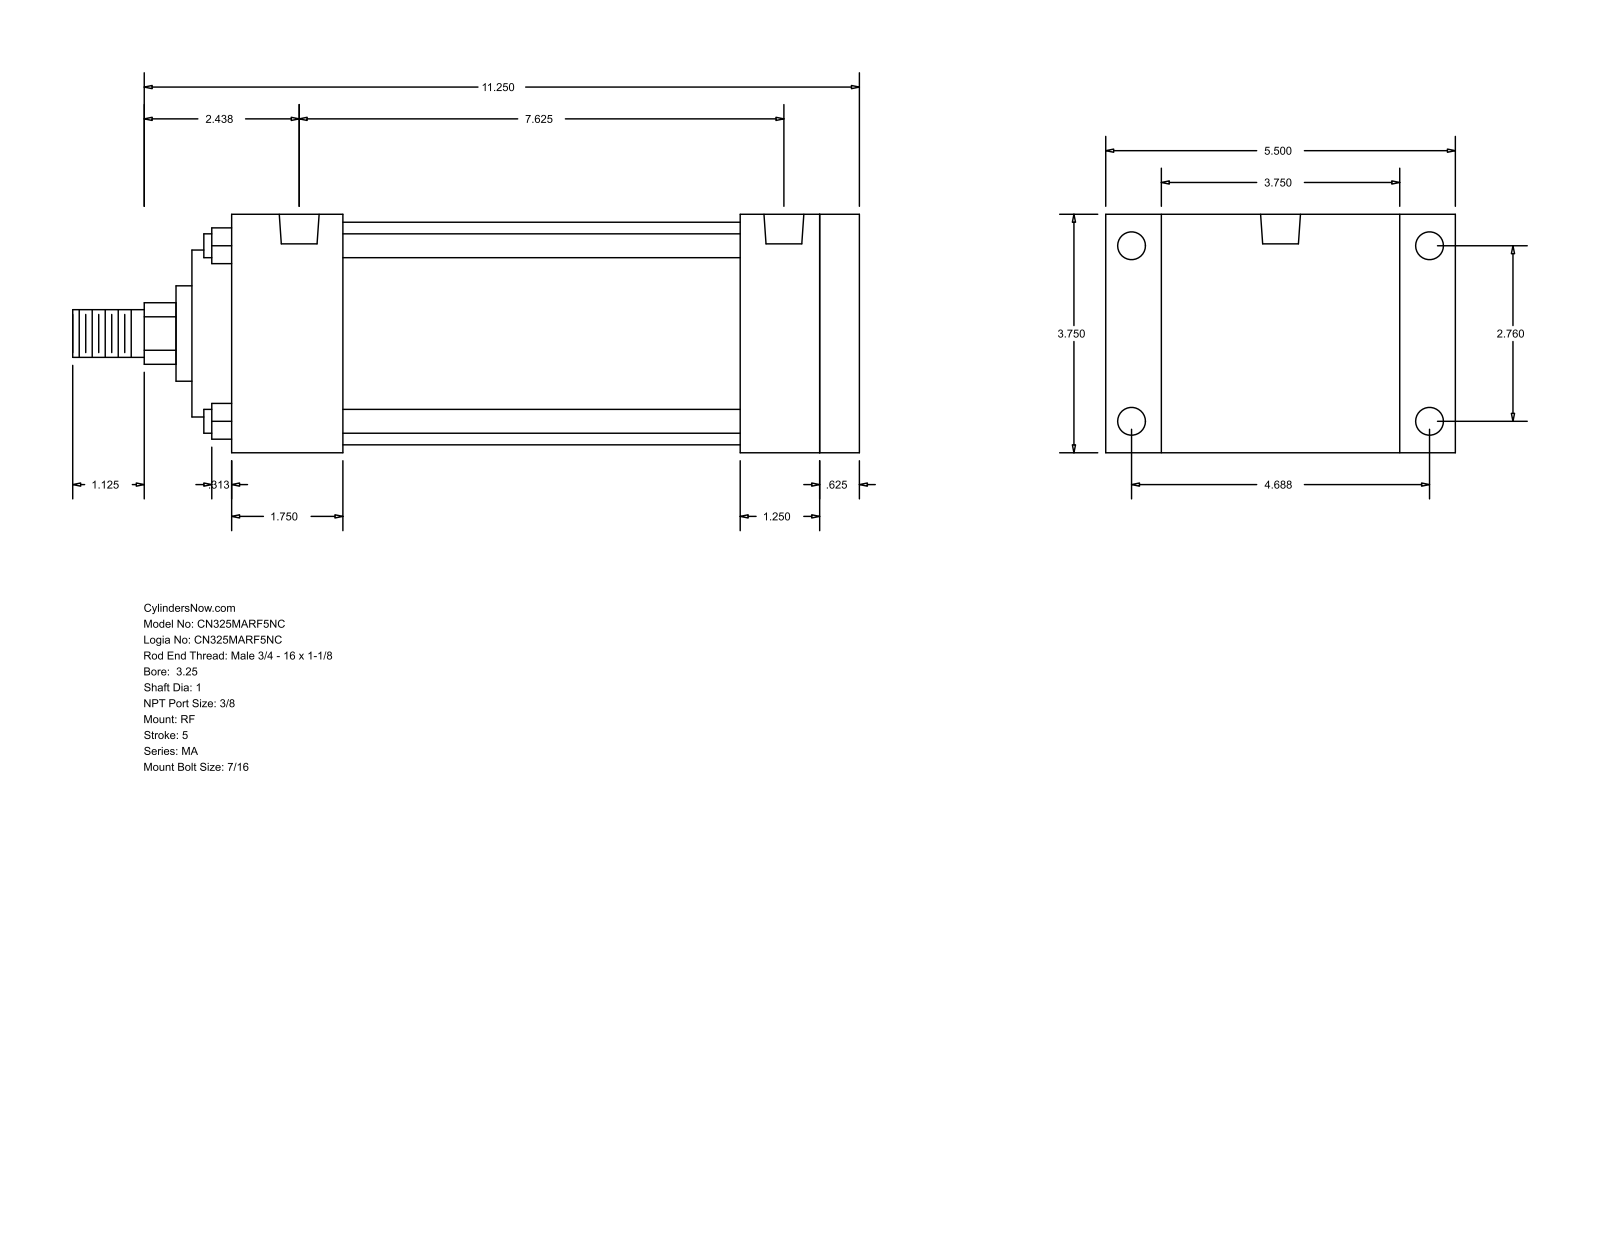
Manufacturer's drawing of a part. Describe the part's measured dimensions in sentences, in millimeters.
The part is named "MA_RF__0325_1". Its 3-D file was written by "GSSL Pune (CONFIG_CONTROL_DESIGN)". It is 0 solids with 94 faces: 65 planar, 29 cylindrical and 0 other. Overall it measures 314.32 by 139.7 by 95.25 millimeters. Round holes: 8 of diameter 11.11, 2 of diameter 15.93. Round bosses or shafts: 4 of diameter 9.53, 1 of diameter 88.9, 1 of diameter 66.67, 1 of diameter 38.1, 1 of diameter 25.4, 1 of diameter 19.05. Partial cylindrical surfaces (rounded edges, fillets, slot ends): 1 of radius 12.29. The main face-to-face distances are 95.24, 250.83, 15.87, 234.96, 22.23, 117.47, 203.2, 31.76, 47.63, 44.46. The hole center spacings are 70.1, 119.06, 138.16, 184.15, 4.76, 4.77, 188.91, 188.92.
